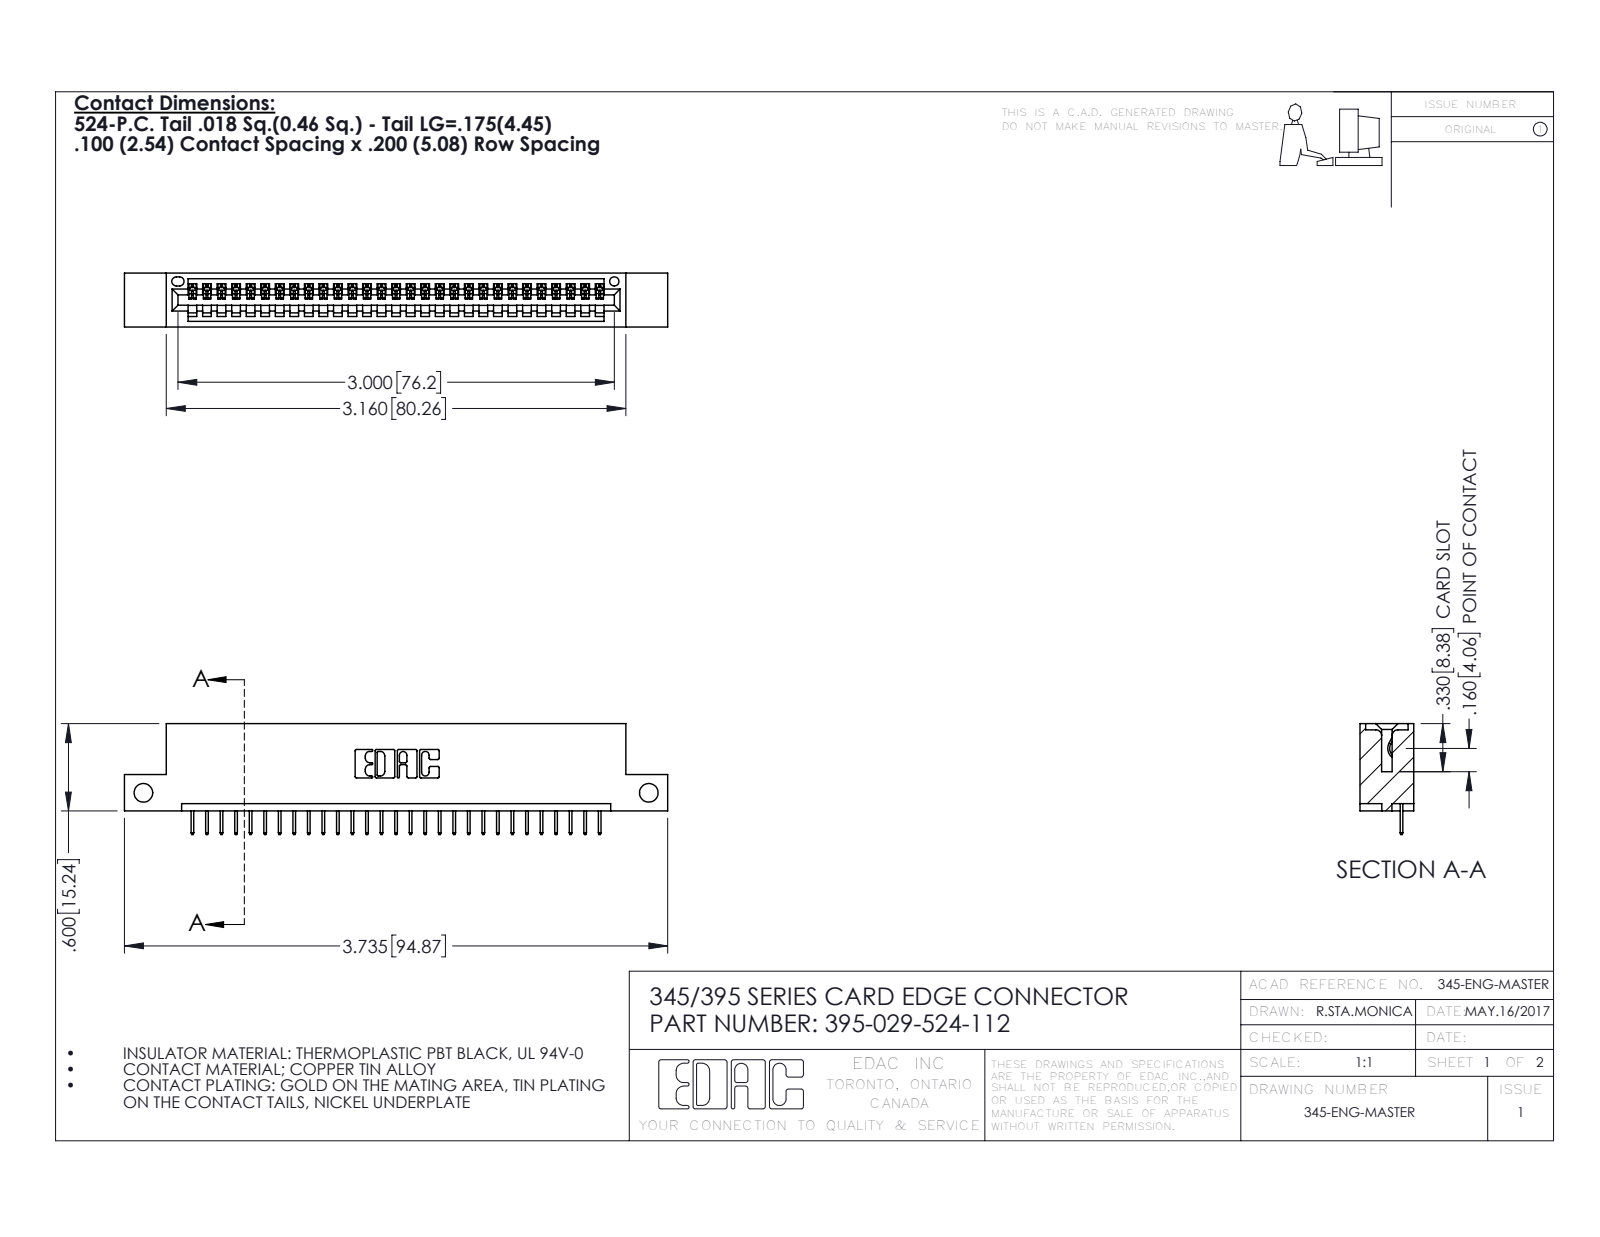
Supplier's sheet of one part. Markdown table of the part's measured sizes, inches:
| quantity | value |
| --- | --- |
| part name | 345-292-001_345-293-124; 345 Part_Flush Mounting Lugs - Side Mount; 395-029-524-112 |
| STEP written by | SolidWorks 2016 (CONFIG_CONTROL_DESIGN) |
| units | inches |
| bodies | 30 solids, 1924 faces (1414 planar, 510 cylindrical, 0 other) |
| overall size | 3.735 × 0.762 × 0.37 |
| volume | 0.531 in³ |
| surface area | 16.86 in² |
| round holes (diameter × count) | 0.128 × 2, 0.064 × 1 |
| partial cylindrical surfaces (radius × count) | 0.006 × 58, 0.01 × 22, 0.007 × 6, 0.031 × 6, 0.026 × 3, 0.031 × 2, 0.04 × 2, 0.014 × 1 |
| main face-to-face distances | 0.298, 0.072, 0.37, 0.2, 0.098, 0.272, 0.025, 0.225, 0.072, 0.149 |
| hole center spacings | 3.475 |
